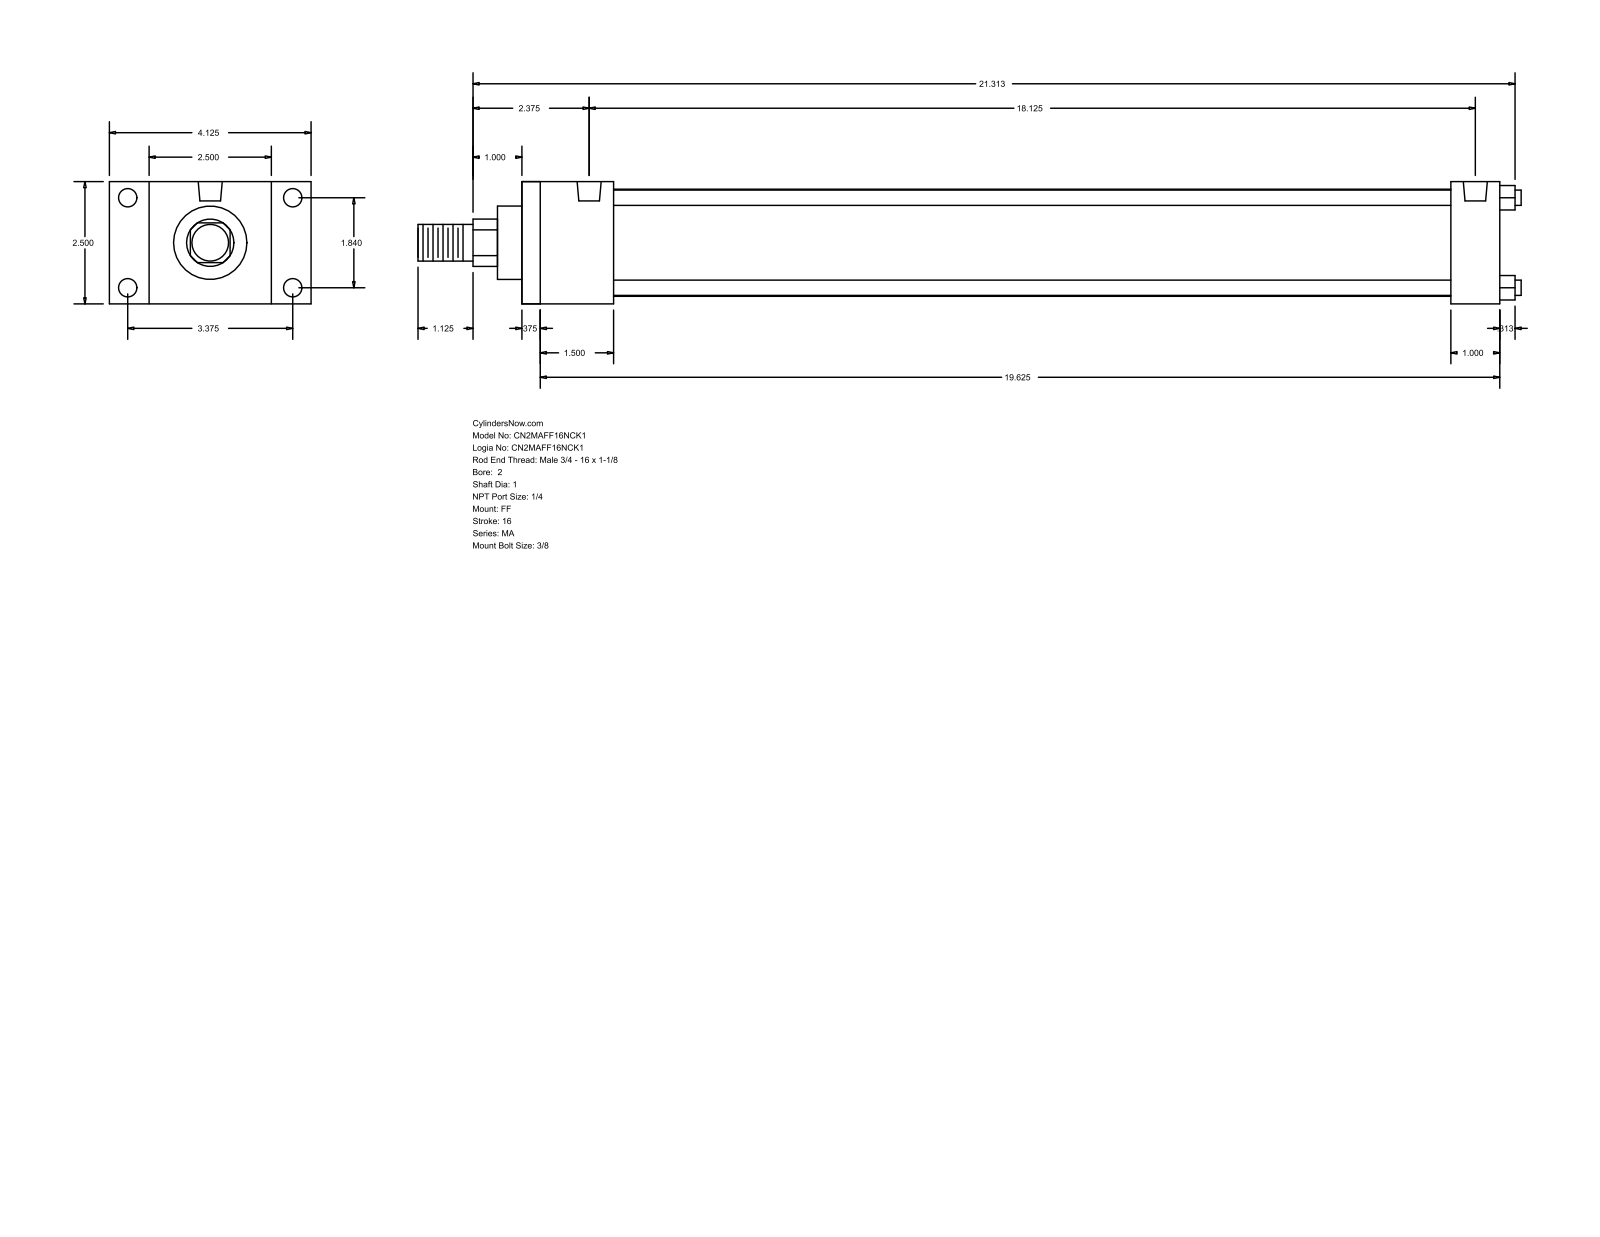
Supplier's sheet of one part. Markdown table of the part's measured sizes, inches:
| quantity | value |
| --- | --- |
| part name | MA_FF__0200_1 |
| STEP written by | GSSL Pune (CONFIG_CONTROL_DESIGN) |
| units | inches |
| bodies | 0 solids, 92 faces (64 planar, 28 cylindrical, 0 other) |
| overall size | 22.563 × 4.125 × 2.5 |
| round holes (diameter × count) | 0.313 × 4, 0.375 × 4, 0.492 × 2 |
| round bosses / shafts (diameter × count) | 0.313 × 4, 2.19 × 1, 1.5 × 1, 1 × 1, 0.75 × 1 |
| partial cylindrical surfaces (radius × count) | 0.484 × 1 |
| main face-to-face distances | 2.5, 20, 0.375, 19.625, 1, 0.813, 0.5, 1.875, 19, 1.5 |
| hole center spacings | 1.84, 3.375, 3.844, 18.125 |
